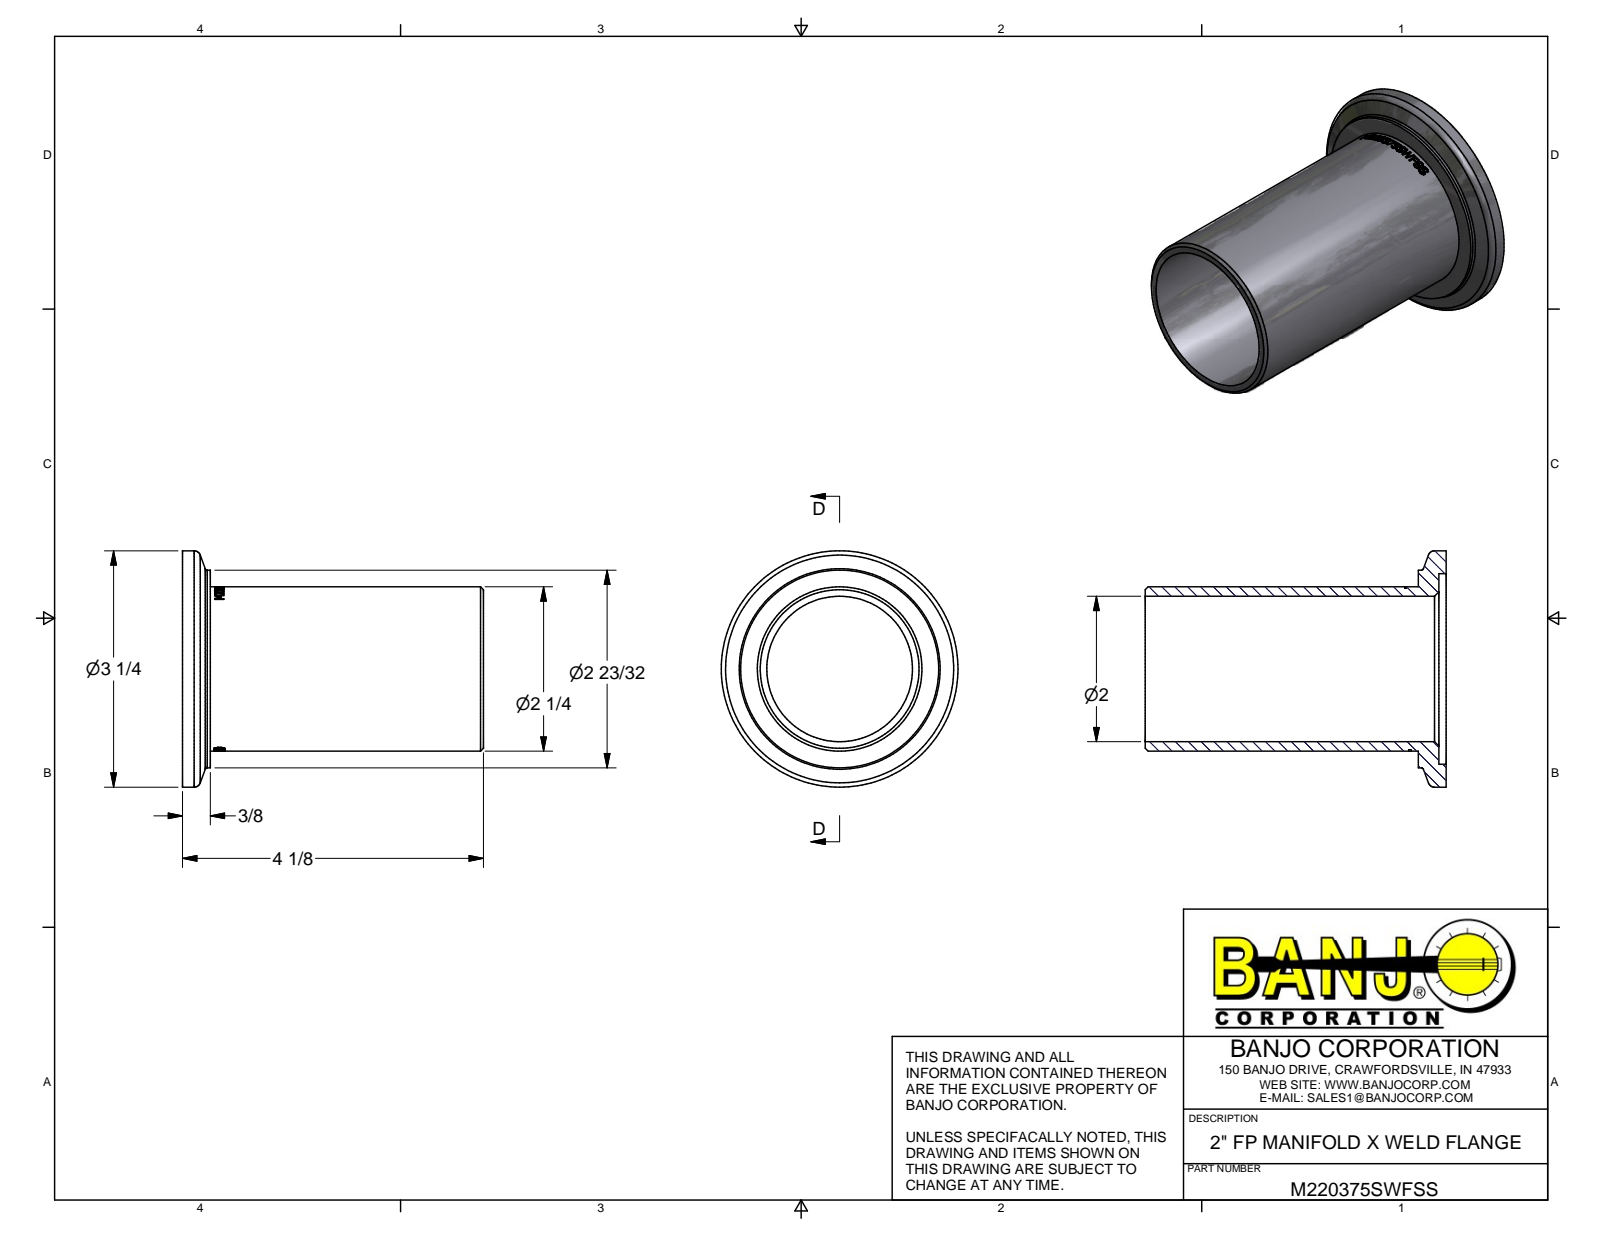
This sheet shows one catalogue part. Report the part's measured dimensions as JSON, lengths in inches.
{"part_name": "M220375SWFSS", "step_written_by": "Autodesk Inventor 2014 (AUTOMOTIVE_DESIGN)", "units": "inches", "bodies": {"solids": 1, "faces": 298, "planar": 122, "cylindrical": 27, "other": 149}, "overall_size": [4.131, 3.25, 3.25], "volume_in3": 4.697, "surface_area_in2": 65.69, "round_holes": [[2, 1], [2.62, 1]], "round_bosses_or_shafts": [[3.25, 1], [2.719, 1], [2.26, 1]], "partial_cylinders_radius": [[1.11, 1]], "face_to_face_distances": [0.1, 0.381, 0.281, 4.131, 4.031, 3.75, 0.019, 0.444, 0.344, 0.063]}
